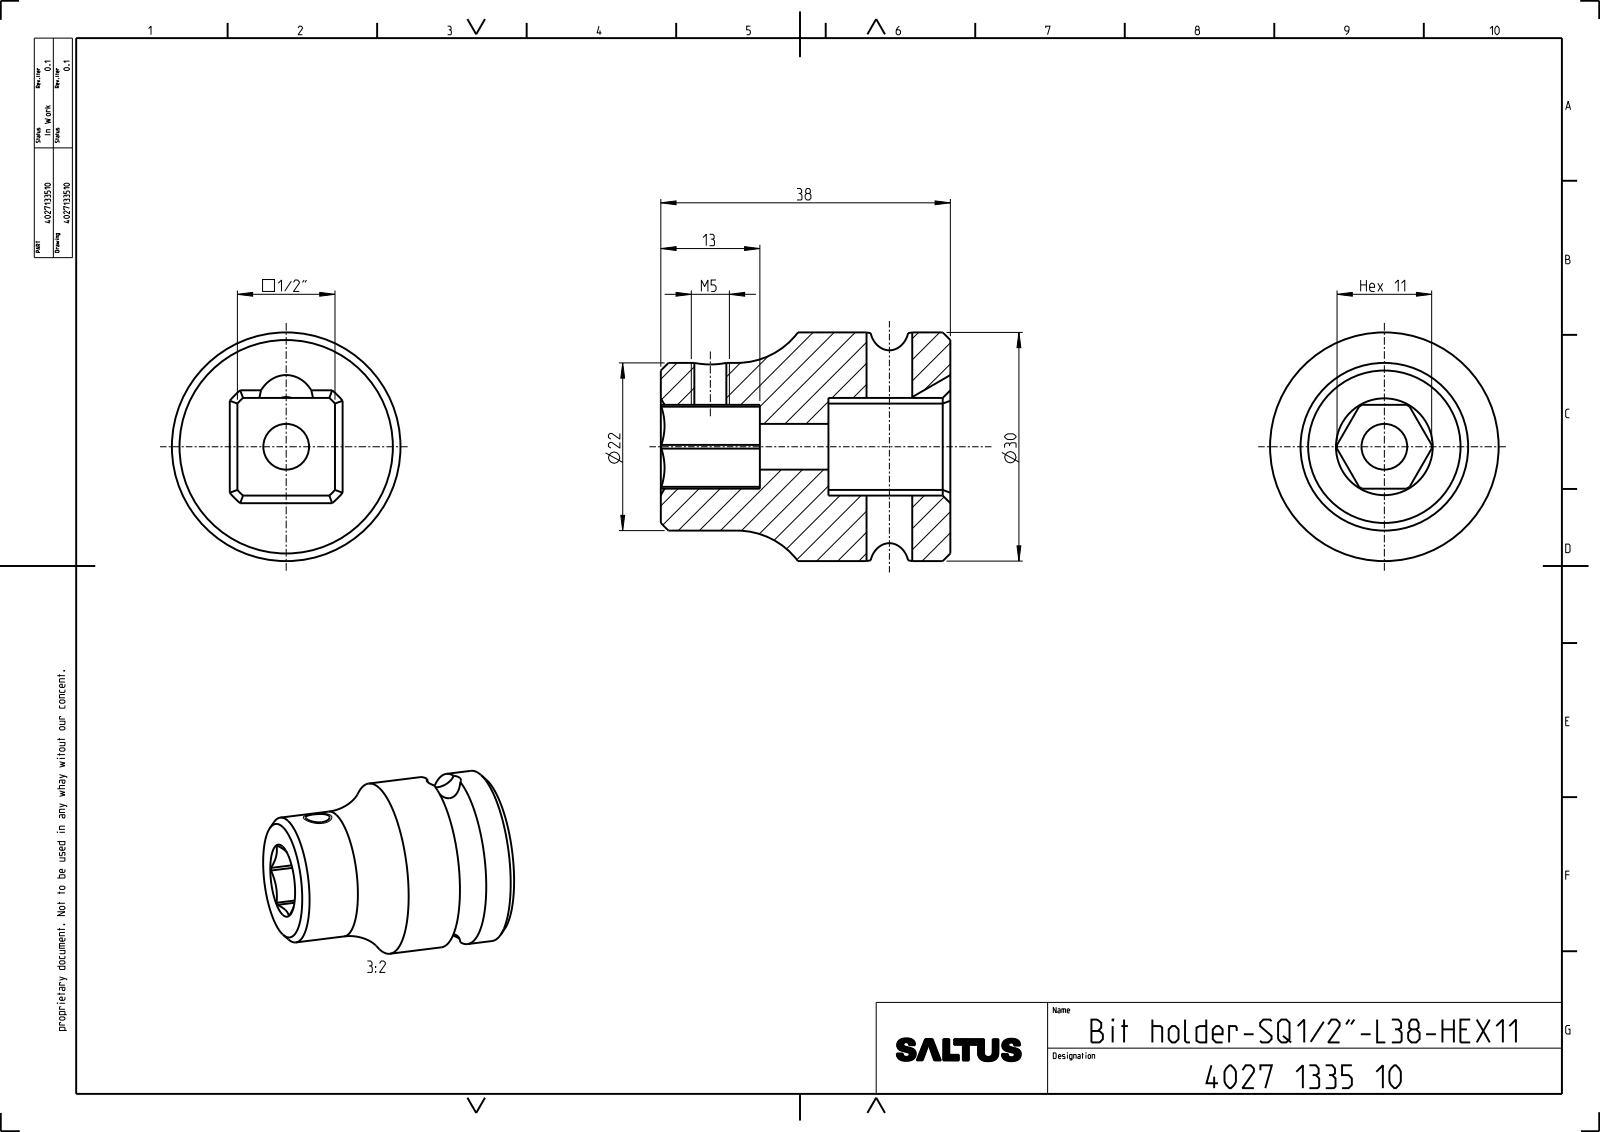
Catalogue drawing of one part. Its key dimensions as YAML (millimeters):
part_name: "4027133510"
step_written_by: "CREO PARAMETRIC BY PTC INC, 2022414 (CONFIG_CONTROL_DESIGN)"
units: millimeters
bodies: {solids: 1, faces: 60, planar: 19, cylindrical: 27, other: 14}
overall_size: [38, 30, 30]
volume: 16222
surface_area: 6051
round_holes:
  - {diameter: 6, count: 2}
  - {diameter: 4.2, count: 1}
  - {diameter: 5, count: 1}
round_bosses_or_shafts:
  - {diameter: 30, count: 1}
  - {diameter: 22, count: 1}
partial_cylinders:
  - {radius: 4, count: 1}
  - {radius: 6.21, count: 1}
  - {radius: 8.55, count: 1}
face_to_face_distances: [12.82, 11, 38, 16, 22, 0.91, 11.91, 25, 9, 13]
hole_center_spacings: [23.5]
